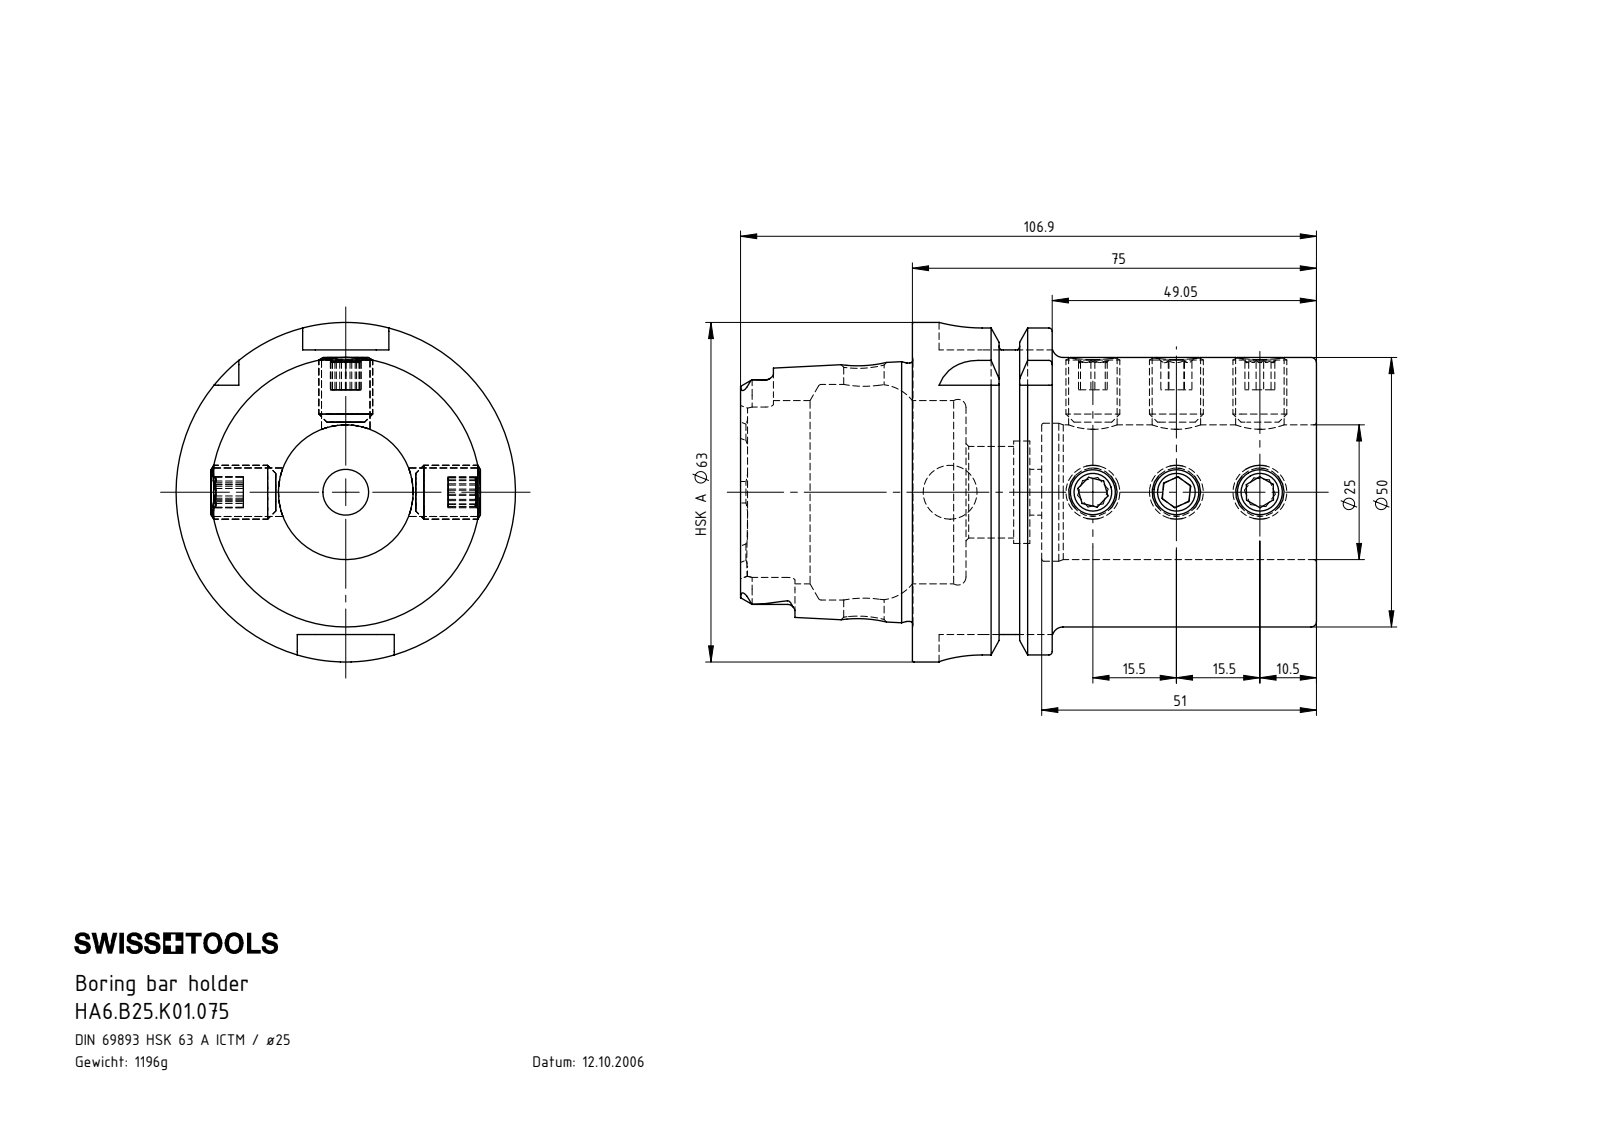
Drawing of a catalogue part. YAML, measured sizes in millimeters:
part_name: "HA6.B25.K01.075; ISO 4026 - M10 x 12; HA6-B25.K01.075_B_Fertigbearbeitung"
step_written_by: "SolidWorks 2017 (AUTOMOTIVE_DESIGN)"
units: millimeters
bodies: {solids: 10, faces: 347, planar: 129, cylindrical: 85, other: 133}
overall_size: [106.9, 63, 63]
volume: 152298
surface_area: 41031
round_holes:
  - {diameter: 9, count: 6}
  - {diameter: 7.5, count: 1}
  - {diameter: 8.5, count: 1}
  - {diameter: 10, count: 1}
  - {diameter: 17, count: 1}
  - {diameter: 19, count: 1}
  - {diameter: 25, count: 1}
  - {diameter: 25.6, count: 1}
  - {diameter: 34, count: 1}
  - {diameter: 40, count: 1}
round_bosses_or_shafts:
  - {diameter: 10, count: 6}
  - {diameter: 63, count: 1}
  - {diameter: 54.95, count: 1}
  - {diameter: 50, count: 1}
  - {diameter: 47.94, count: 1}
partial_cylinders:
  - {radius: 1.4, count: 6}
  - {radius: 8, count: 4}
  - {radius: 2.88, count: 2}
  - {radius: 2.82, count: 1}
  - {radius: 2.82, count: 1}
face_to_face_distances: [75, 16, 25.95, 49.05, 9.95, 65.05, 24, 14.05, 1.95, 51]
hole_center_spacings: [15.5, 31, 26.5, 42, 42.5, 57.5, 58, 73.5]
